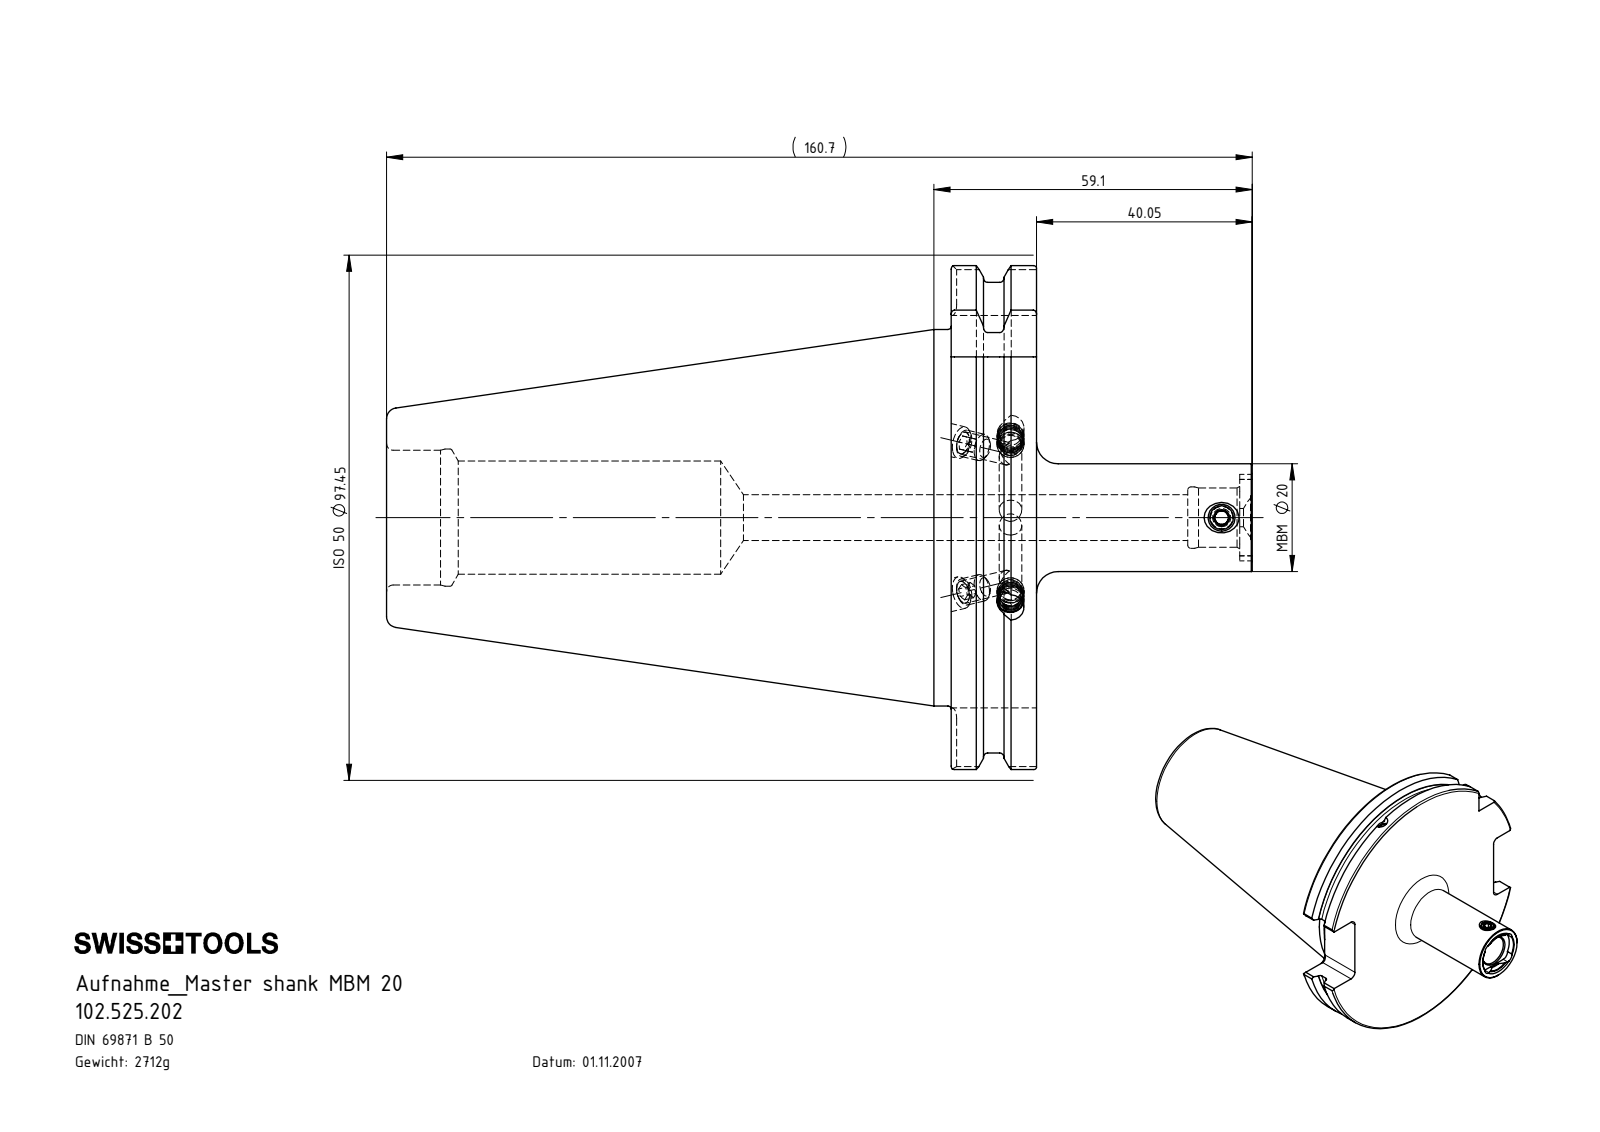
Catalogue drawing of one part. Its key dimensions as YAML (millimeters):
part_name: "KVT_MB_600_050; ISO 4026 - M5 x 5_PreviewCfg; 102.525.202; MB1-ER1.001.006_A (+1 more)"
step_written_by: "SolidWorks 2017 (CONFIG_CONTROL_DESIGN)"
units: millimeters
bodies: {solids: 8, faces: 300, planar: 77, cylindrical: 82, other: 141}
overall_size: [160.7, 97.45, 93.51]
volume: 345428
surface_area: 46869
round_holes:
  - {diameter: 4.2, count: 4}
  - {diameter: 4, count: 2}
  - {diameter: 6, count: 2}
  - {diameter: 2.5, count: 1}
  - {diameter: 5, count: 1}
  - {diameter: 8.5, count: 1}
  - {diameter: 11, count: 1}
  - {diameter: 11.4, count: 1}
  - {diameter: 21, count: 1}
  - {diameter: 25, count: 1}
  - {diameter: 25.45, count: 1}
round_bosses_or_shafts:
  - {diameter: 5, count: 4}
  - {diameter: 91, count: 1}
  - {diameter: 69.85, count: 1}
  - {diameter: 20, count: 1}
partial_cylinders:
  - {radius: 2, count: 8}
  - {radius: 2.2, count: 4}
  - {radius: 6.5, count: 1}
  - {radius: 8.03, count: 1}
  - {radius: 48.73, count: 1}
face_to_face_distances: [15.85, 104.8, 120.65, 72.8, 25.7, 42.7, 17, 7.65, 65.15, 160.7]
